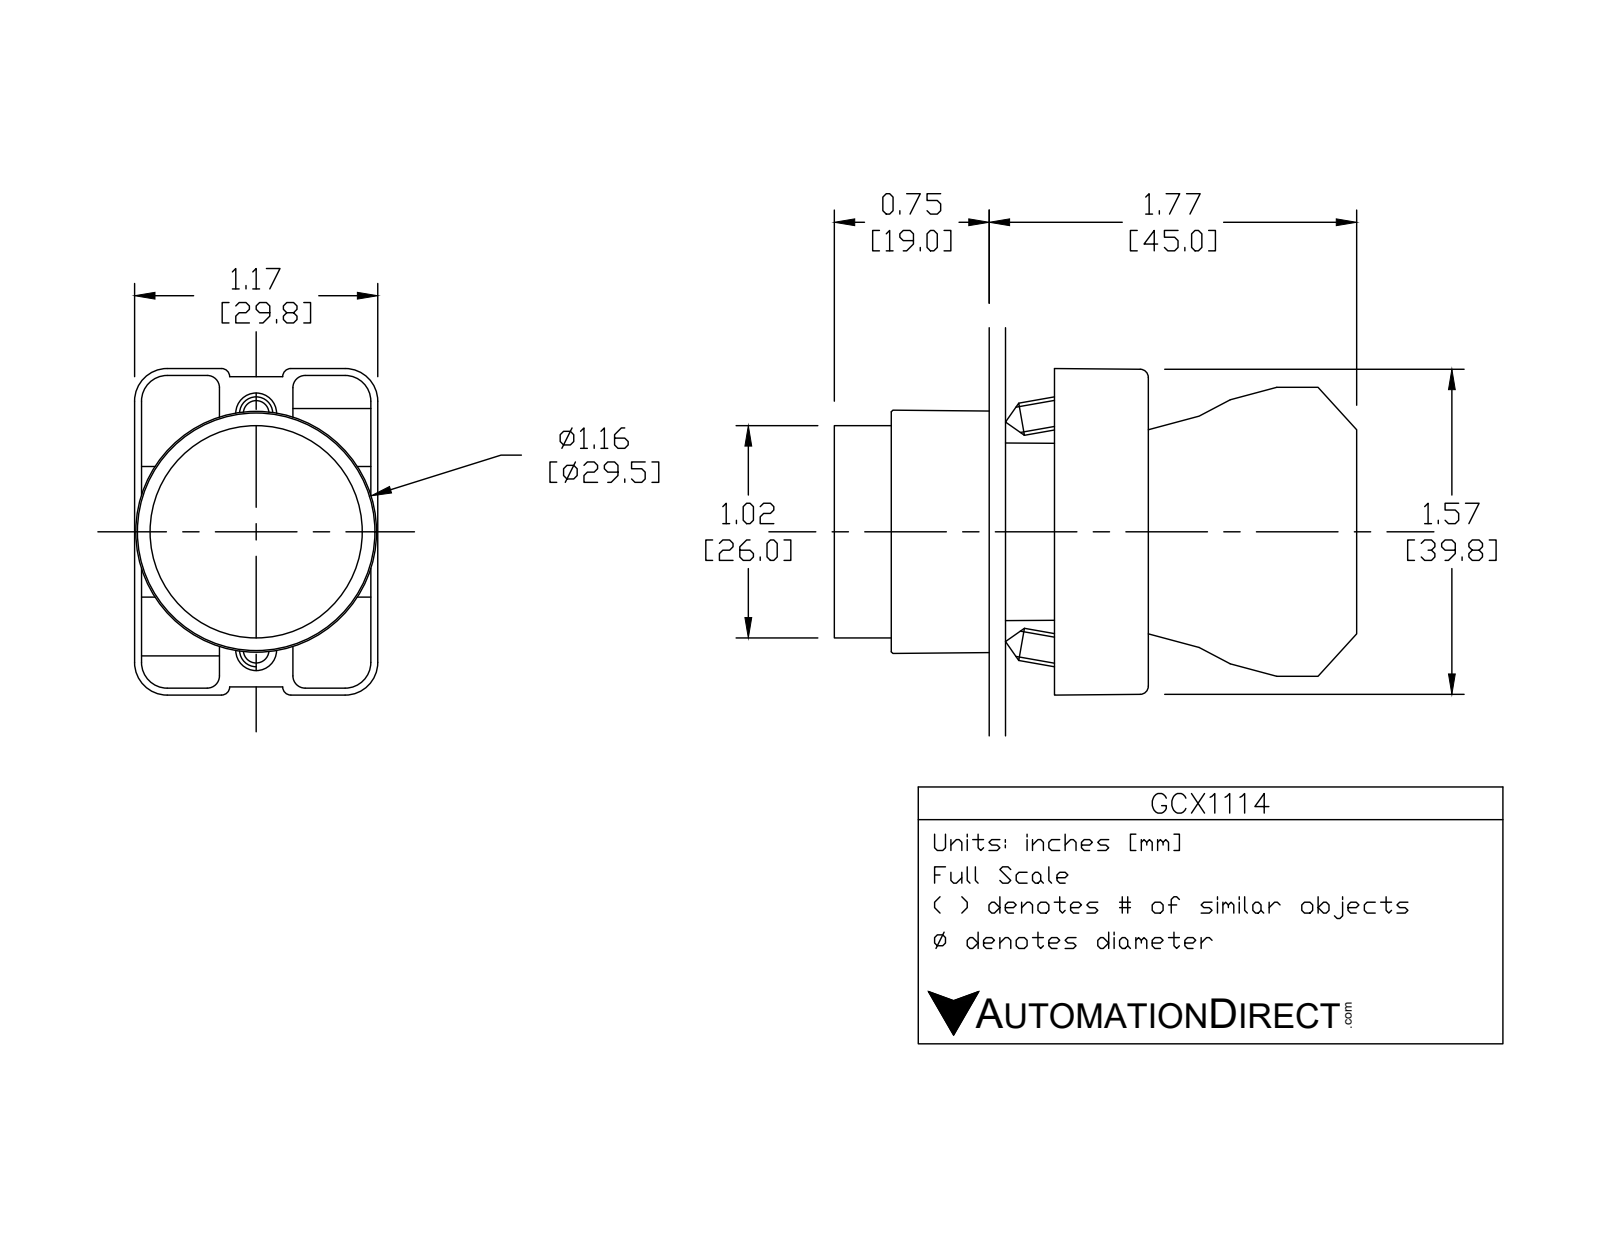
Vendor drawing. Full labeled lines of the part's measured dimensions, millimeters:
Part name (STEP PRODUCT): GCX1114; ecx1040; GCX1114 OPERATOR; ecx1029
STEP written by: SolidWorks 2016 (AUTOMOTIVE_DESIGN)
Units: millimetres
Bodies: 6 solids, 383 faces (222 planar, 132 cylindrical, 29 other)
Overall size (bounding box): 63.3 × 40.2 × 29.9
Volume: 25 960 mm³ · Surface area: 17 080 mm²
Round holes (diameter × count): ⌀2 ×2, ⌀3.1 ×2, ⌀3.3 ×2, ⌀2.2 ×1, ⌀5 ×1, ⌀22.3 ×1, ⌀22.6 ×1, ⌀26 ×1
Round bosses / shafts (diameter × count): ⌀4 ×2, ⌀29.8 ×1, ⌀25.5 ×1, ⌀24 ×1, ⌀21.7 ×1, ⌀19.8 ×1
Partial cylindrical surfaces — rounded edges, fillets, slot ends (radius × count): R1.5 ×24, R1 ×12, R3.1 ×12, R4 ×12, R1 ×4, R3.3 ×2, R0.5 ×1, R1.6 ×1
Main face-to-face distances: 14.7, 0.8, 30.3, 0.8, 12, 18.3, 7, 17.5, 15.2, 29.5
Hole centre spacings: 6, 13.8, 12, 12.4
